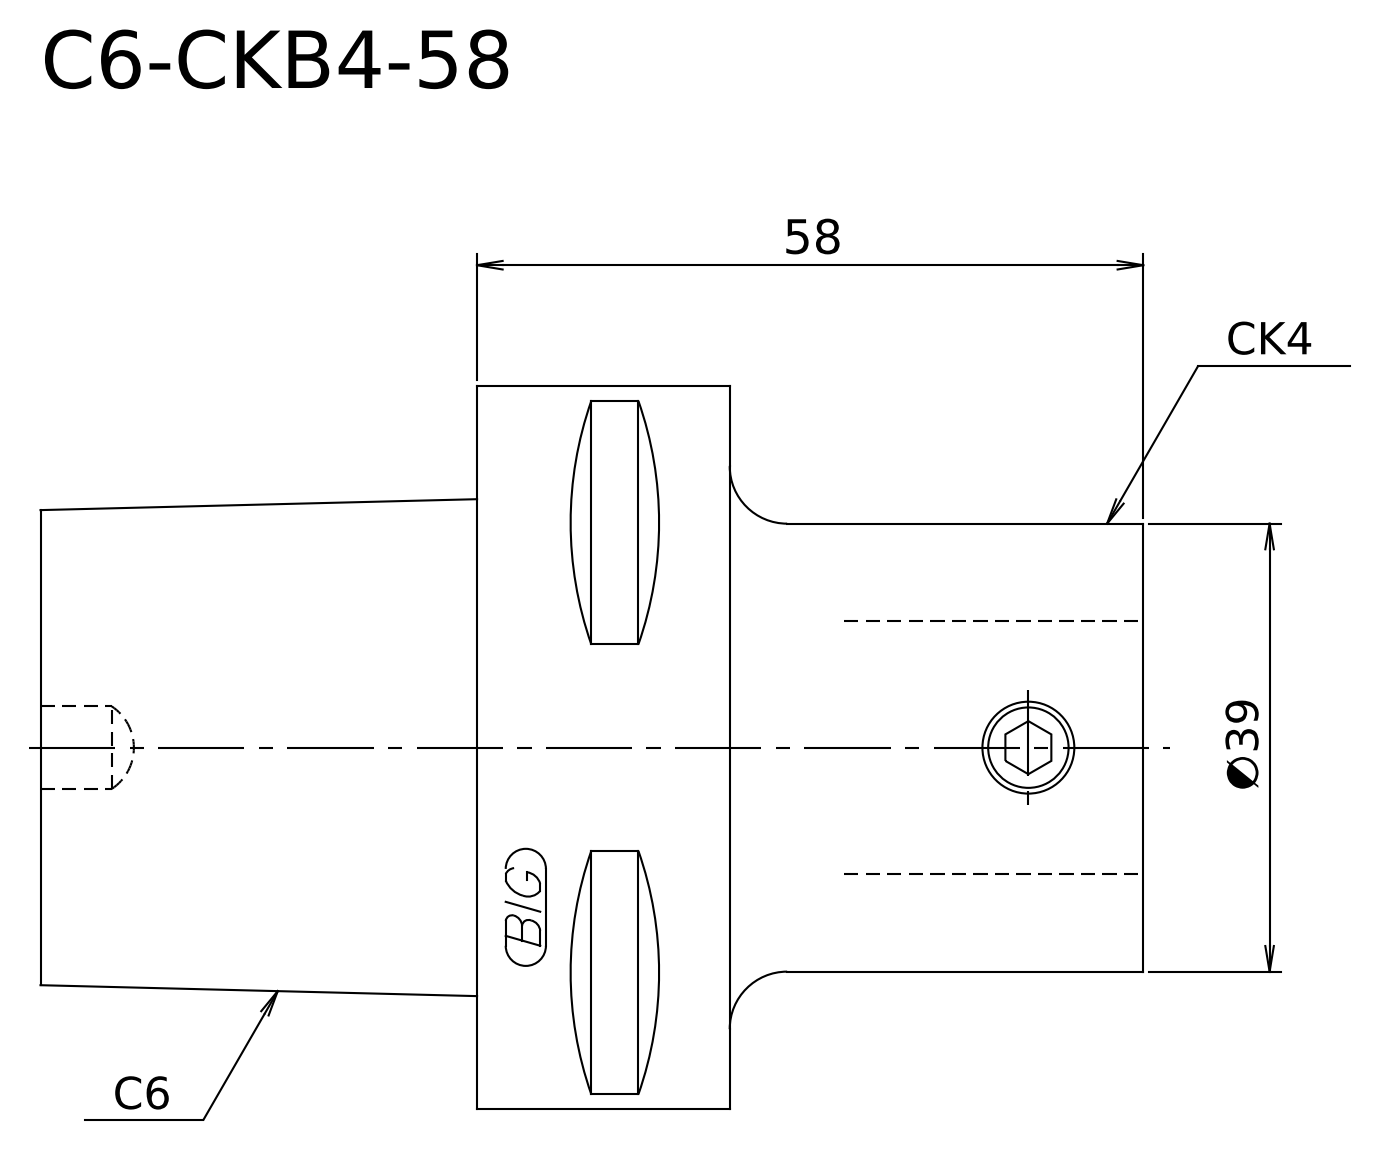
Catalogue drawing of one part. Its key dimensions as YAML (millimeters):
step_written_by: "Kubotek KeyCreator V8.5.1 (14335) (CONFIG_CONTROL_DESIGN)"
units: millimeters
bodies: {solids: 1, faces: 10, planar: 4, cylindrical: 2, other: 4}
overall_size: [96, 62.98, 62.98]
volume: 167993
surface_area: 19698
round_bosses_or_shafts:
  - {diameter: 62.98, count: 1}
  - {diameter: 39, count: 1}
face_to_face_distances: [38, 22, 60, 36, 58, 96]
